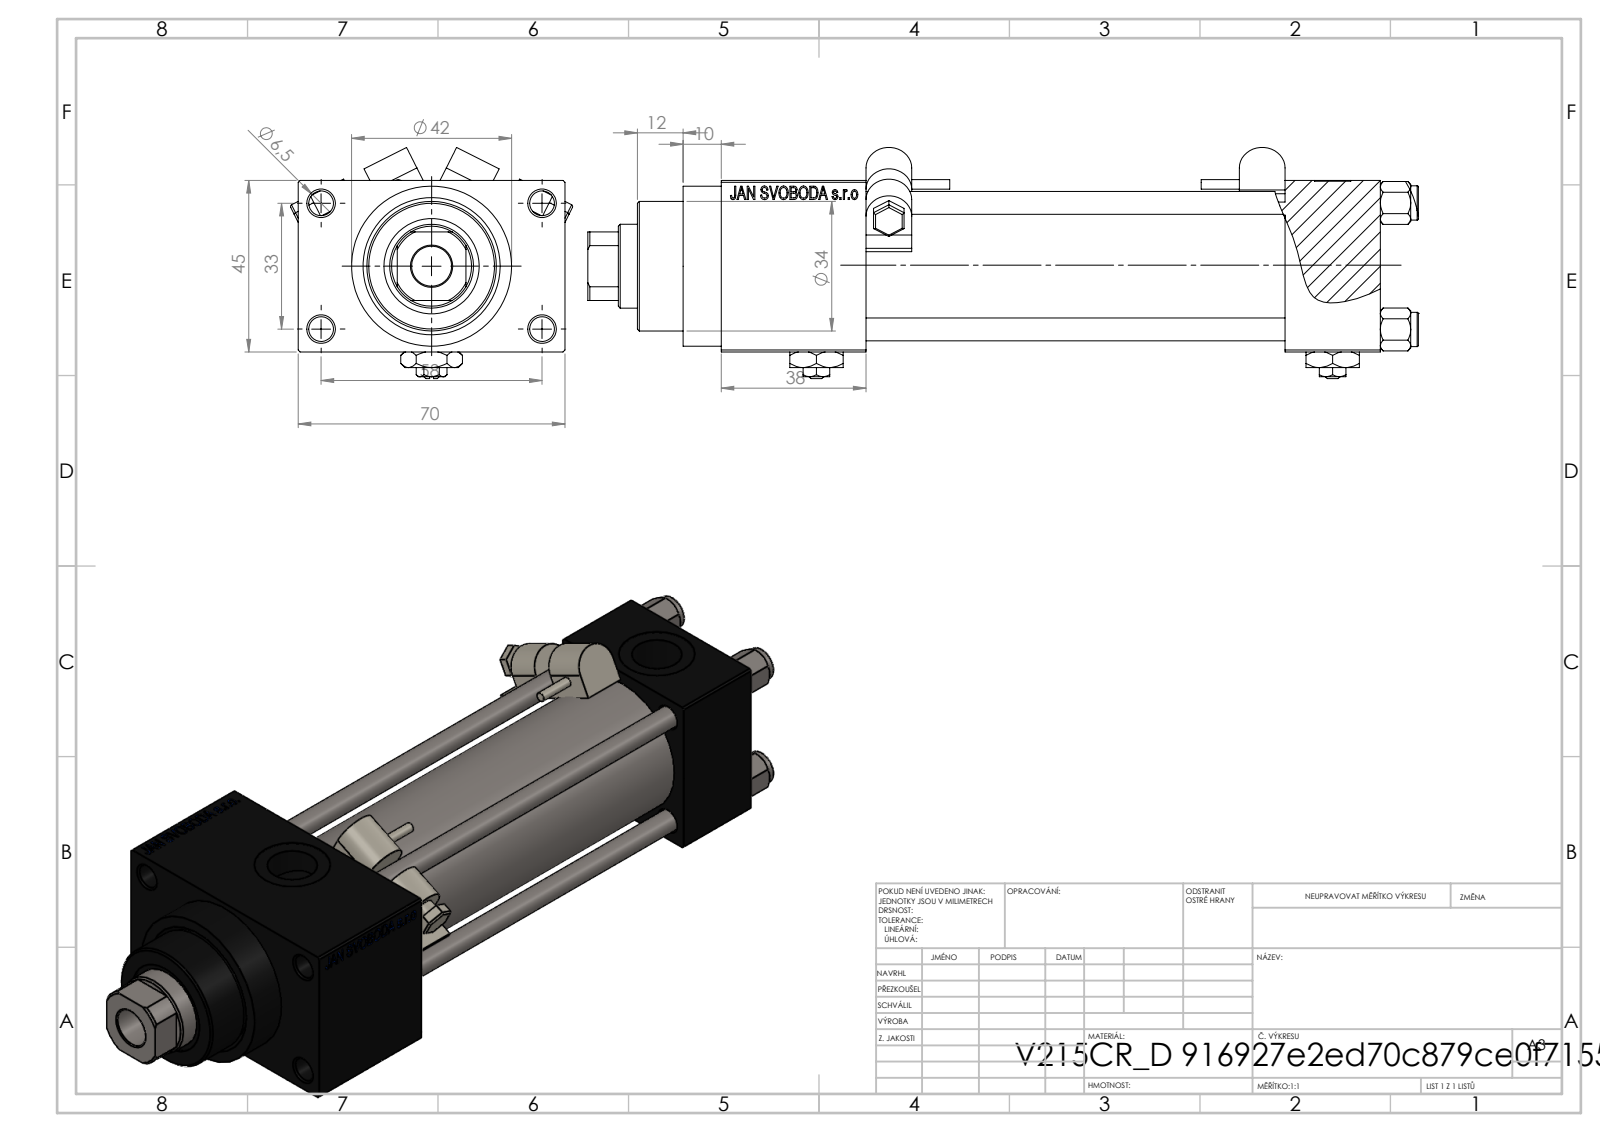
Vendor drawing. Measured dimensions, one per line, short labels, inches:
name: V215_VC_A; MSRF_MSRG1; Zatka_pro_OIL_PORT; V215CR_VCP_D (+3 more)
written by: SolidWorks 2019 (CONFIG_CONTROL_DESIGN)
unit: in
bodies: 15 solids, 1268 faces (578 planar, 128 cylindrical, 562 other)
size: 8.583 × 2.915 × 2.388
volume: 18.28 in³; area: 166.1 in²
holes: 4× ⌀0.236, 4× ⌀0.256, 2× ⌀0.276, 2× ⌀0.518, 2× ⌀0.787, 1× ⌀0.413, 1× ⌀0.866, 1× ⌀0.945, 1× ⌀0.984, 1× ⌀1.26, 1× ⌀1.299
bosses: 4× ⌀0.354, 2× ⌀0.197, 2× ⌀0.098, 1× ⌀1.654, 1× ⌀1.496, 1× ⌀1.339
rounds: 12× R0.02, 4× R0.236, 1× R0.413
face distances: 1.772, 0.984, 0.492, 2.264, 4.331, 5.315, 5.827, 1.496, 2.756, 6.811
hole spacings: 0.488, 0.924, 1.307, 1.314, 1.392, 1.795, 2.219, 1.299
